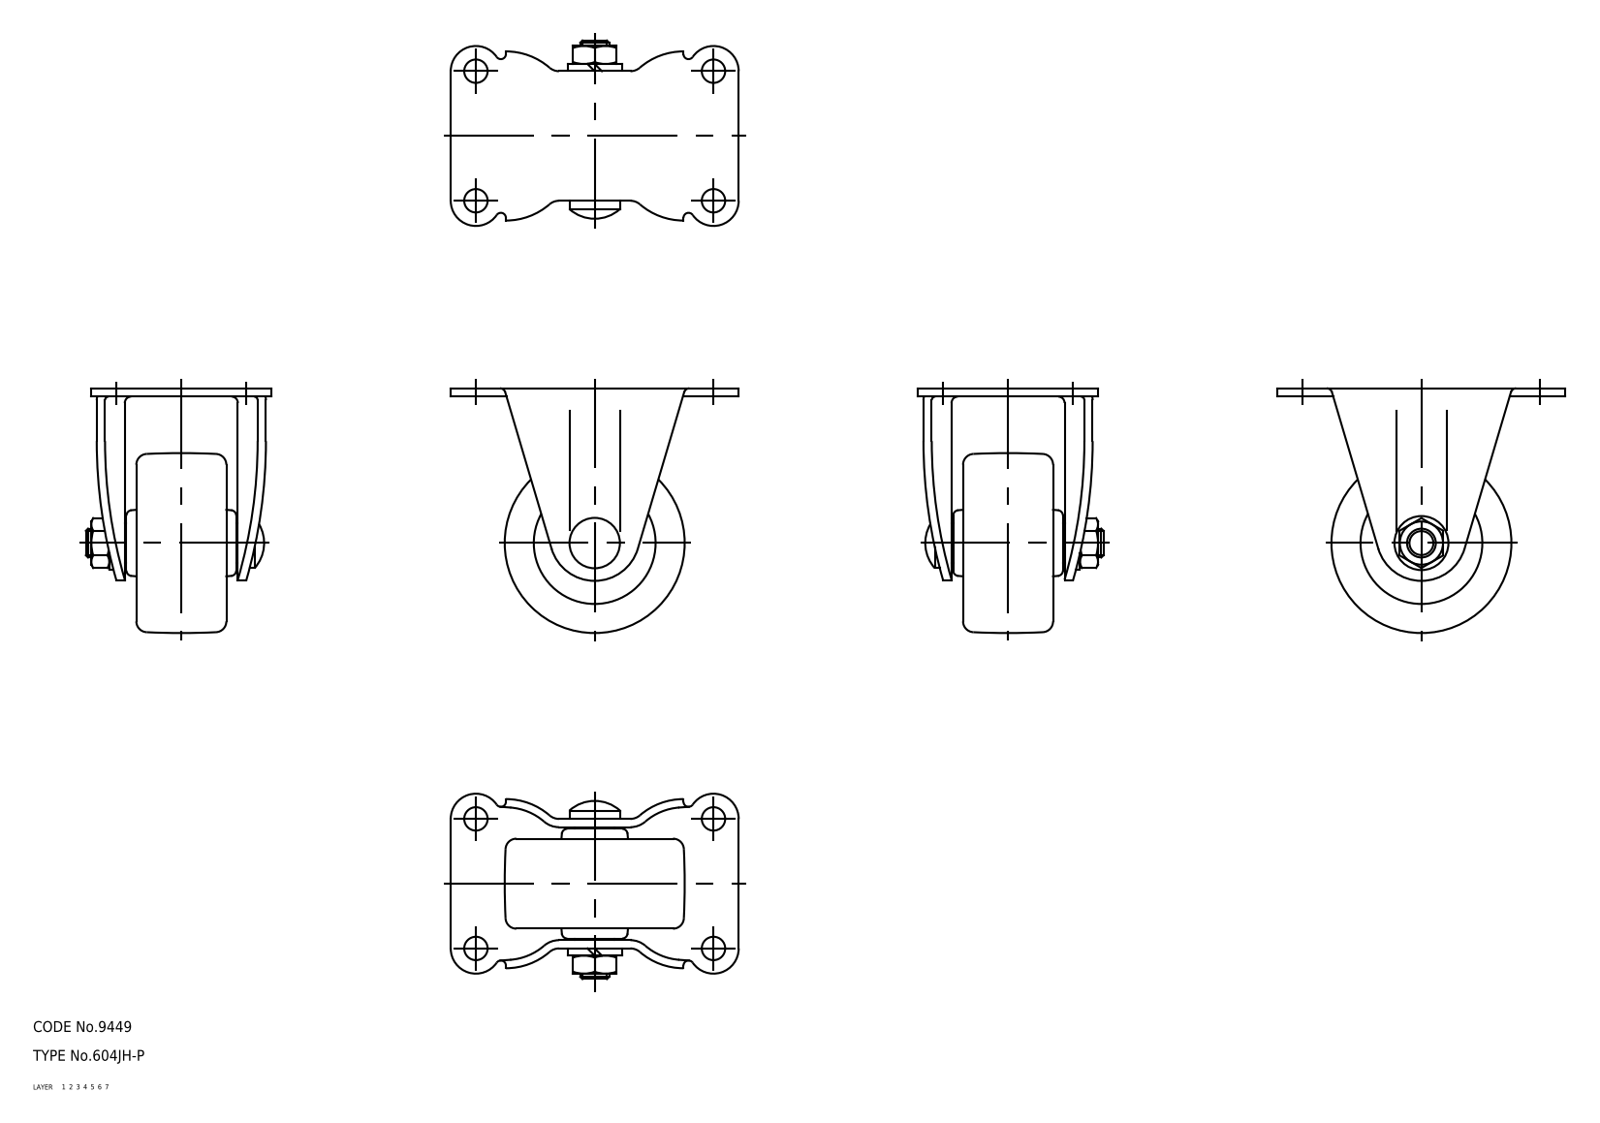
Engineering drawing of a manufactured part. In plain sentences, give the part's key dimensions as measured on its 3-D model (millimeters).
The part is named "wheel; axle; No_604JH_P_14887_36". Its 3-D file was written by "CADfix (AUTOMOTIVE_DESIGN)". It is 3 solids with 175 faces: 0 planar, 0 cylindrical and 175 other. Overall it measures 80 by 68 by 51.5 millimeters. Its volume is 59 366 cubic millimeters and its surface area 26 364 square millimeters.
